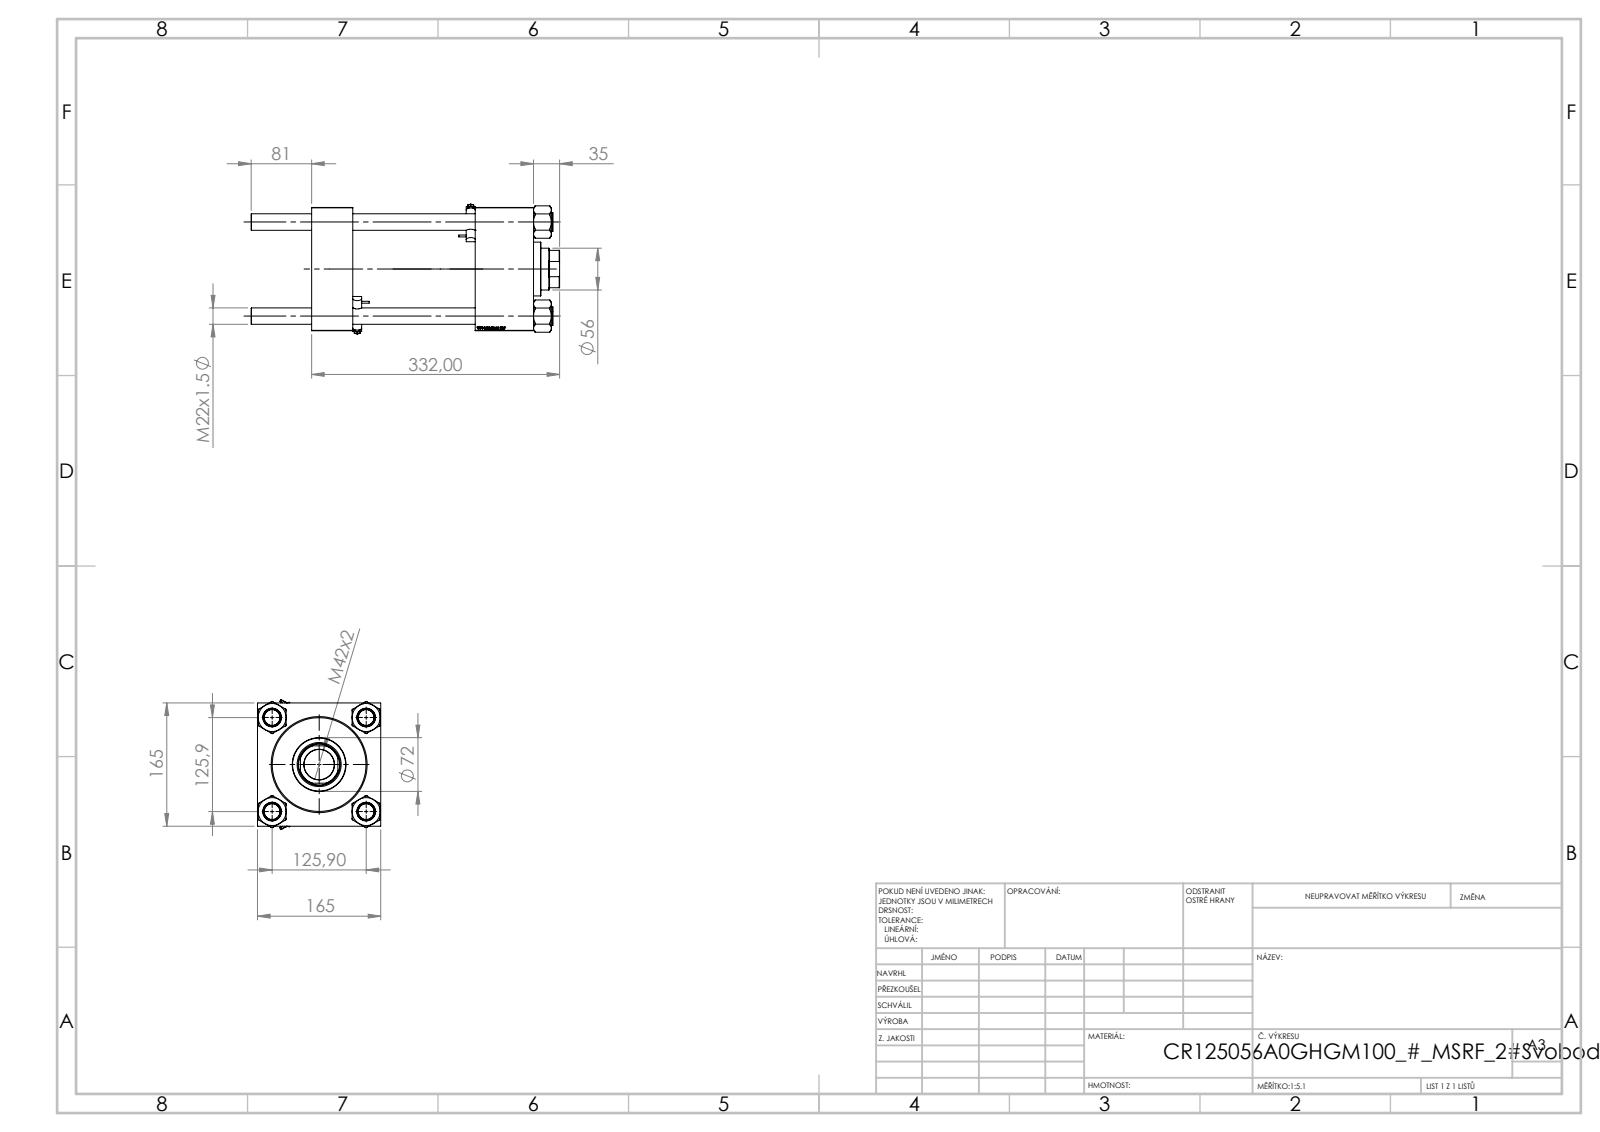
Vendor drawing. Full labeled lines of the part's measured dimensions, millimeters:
Part name (STEP PRODUCT): V215_VC_A; MSRF_MSRG1; CR025_012_A_0_G_A_G_M_020_+#_##_TYCINKA; V215CR_BODY_A (+2 more)
STEP written by: SolidWorks 2019 (CONFIG_CONTROL_DESIGN)
Units: millimetres
Bodies: 13 solids, 1246 faces (604 planar, 106 cylindrical, 536 other)
Overall size (bounding box): 413 × 173.85 × 165
Volume: 5 104 000 mm³ · Surface area: 654 237 mm²
Round holes (diameter × count): ⌀22 ×4, ⌀7 ×2, ⌀32.24 ×2, ⌀45 ×2, ⌀40.5 ×1, ⌀56 ×1, ⌀59 ×1, ⌀96 ×1, ⌀125 ×1, ⌀125.5 ×1
Round bosses / shafts (diameter × count): ⌀25 ×4, ⌀5 ×2, ⌀2.5 ×2, ⌀131 ×1, ⌀72 ×1
Partial cylindrical surfaces — rounded edges, fillets, slot ends (radius × count): R0.5 ×12, R6 ×4, R27 ×1
Main face-to-face distances: 165, 55, 297, 242, 219, 164, 78, 268.3, 213.3, 49.3
Hole centre spacings: 89.02, 125.9, 178.05, 218.5
